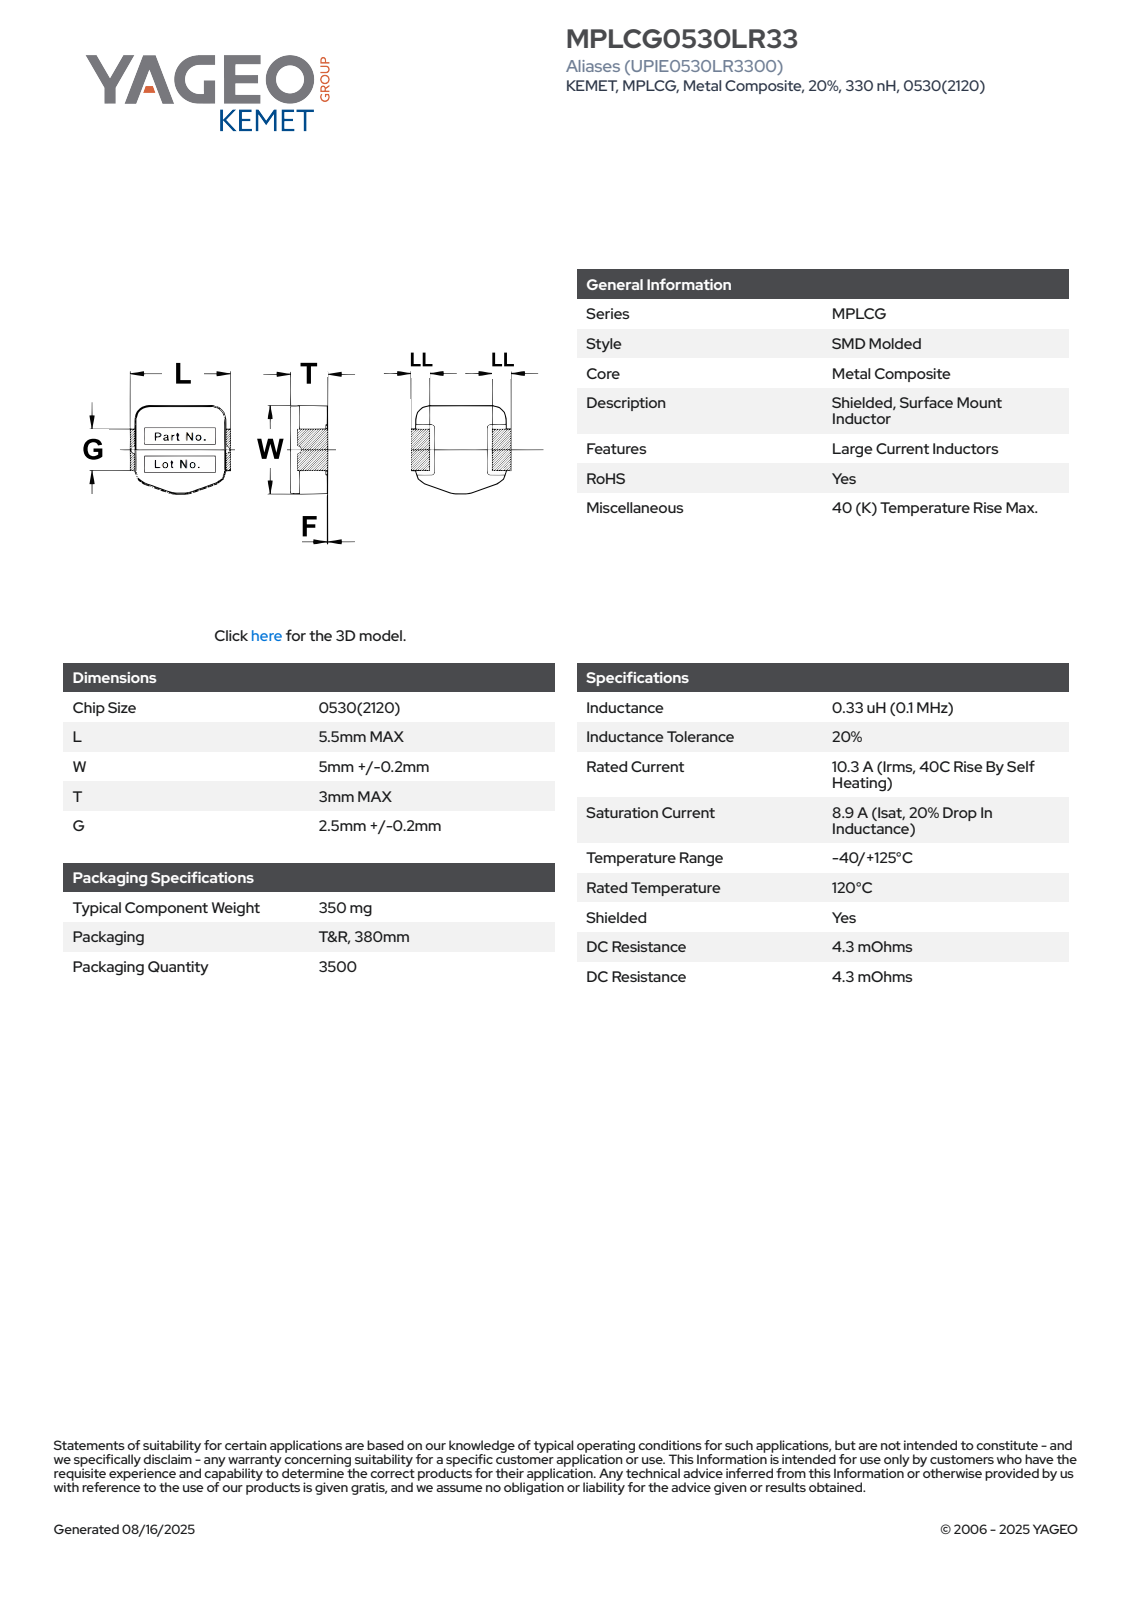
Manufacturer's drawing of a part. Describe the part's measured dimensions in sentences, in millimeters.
The part is named "IS_MPLCG_2220_L5.5W5.2T3LL1.1F0.1G2.7". Its 3-D file was written by "SolidWorks 2014 (AUTOMOTIVE_DESIGN)". It is 4 solids with 116 faces: 95 planar, 21 cylindrical and 0 other. Overall it measures 5.5 by 5.2 by 3 millimeters. Its volume is 73 cubic millimeters and its surface area 131 square millimeters. Partial cylindrical surfaces (rounded edges, fillets, slot ends): 4 of radius 1, 2 of radius 0.6, 1 of radius 0.15. The main face-to-face distances are 3, 5.3, 5.2, 5.4, 5.1, 2.9, 5.5, 1.9, 1, 1.7.
